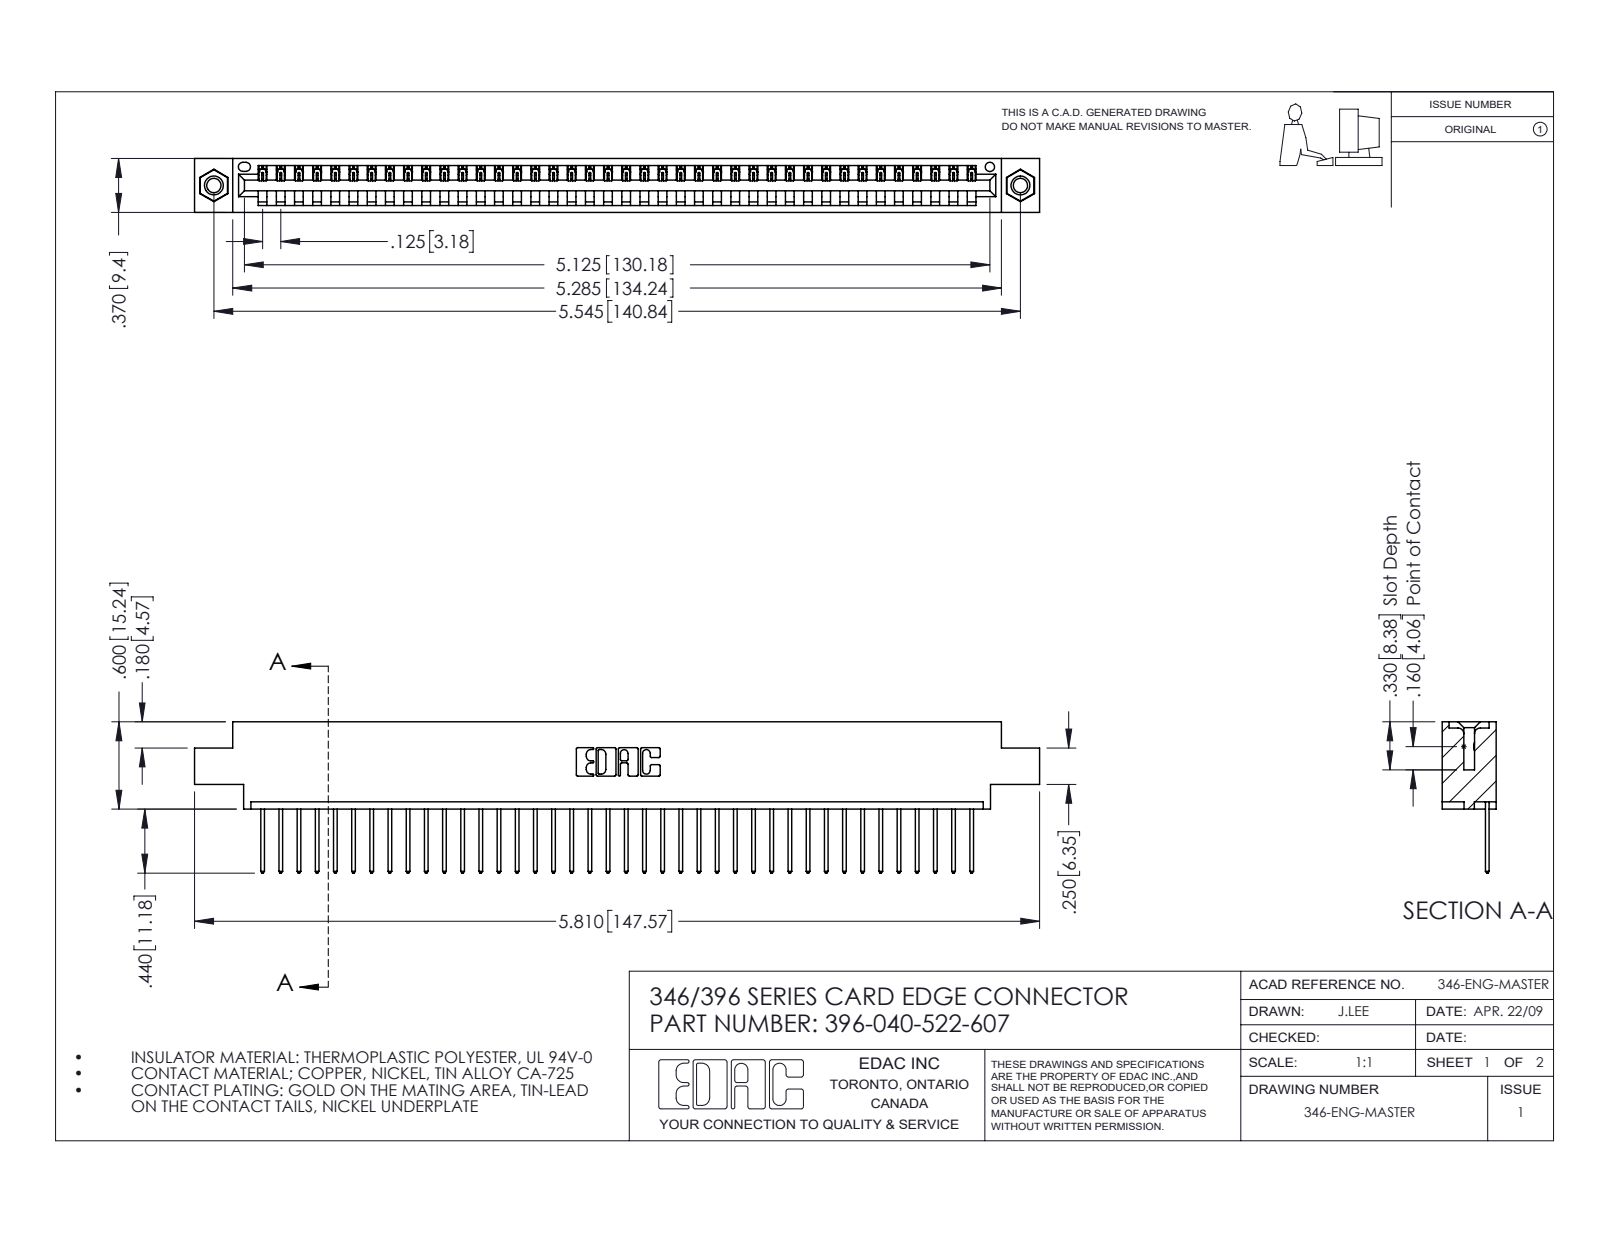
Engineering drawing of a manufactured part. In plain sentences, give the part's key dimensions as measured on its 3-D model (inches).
The part is named "345-250-001_345-250-005-103; 345-292-001_345-293-122; 346 Part_0.170 Offset - 0.156 Dia-TI; 396-040-522-607". Its 3-D file was written by "SolidWorks 2016 (CONFIG_CONTROL_DESIGN)". It is 43 solids with 2506 faces: 1712 planar, 778 cylindrical and 16 other. Overall it measures 5.81 by 1.04 by 0.37 inches. Its volume is 0.851 cubic inches and its surface area 27.52 square inches. Round holes: 2 of diameter 0.098, 2 of diameter 0.125, 2 of diameter 0.156, 1 of diameter 0.064. Round bosses or shafts: 2 of diameter 0.155. Partial cylindrical surfaces (rounded edges, fillets, slot ends): 80 of radius 0.006, 80 of radius 0.01, 22 of radius 0.01, 6 of radius 0.007, 6 of radius 0.031, 3 of radius 0.026, 2 of radius 0.031, 2 of radius 0.04. The main face-to-face distances are 0.048, 0.322, 0.37, 0.25, 0.072, 0.298, 0.025, 0.222, 0.148, 0.1. The hole center spacings are 0.246, 5.336, 5.545.
